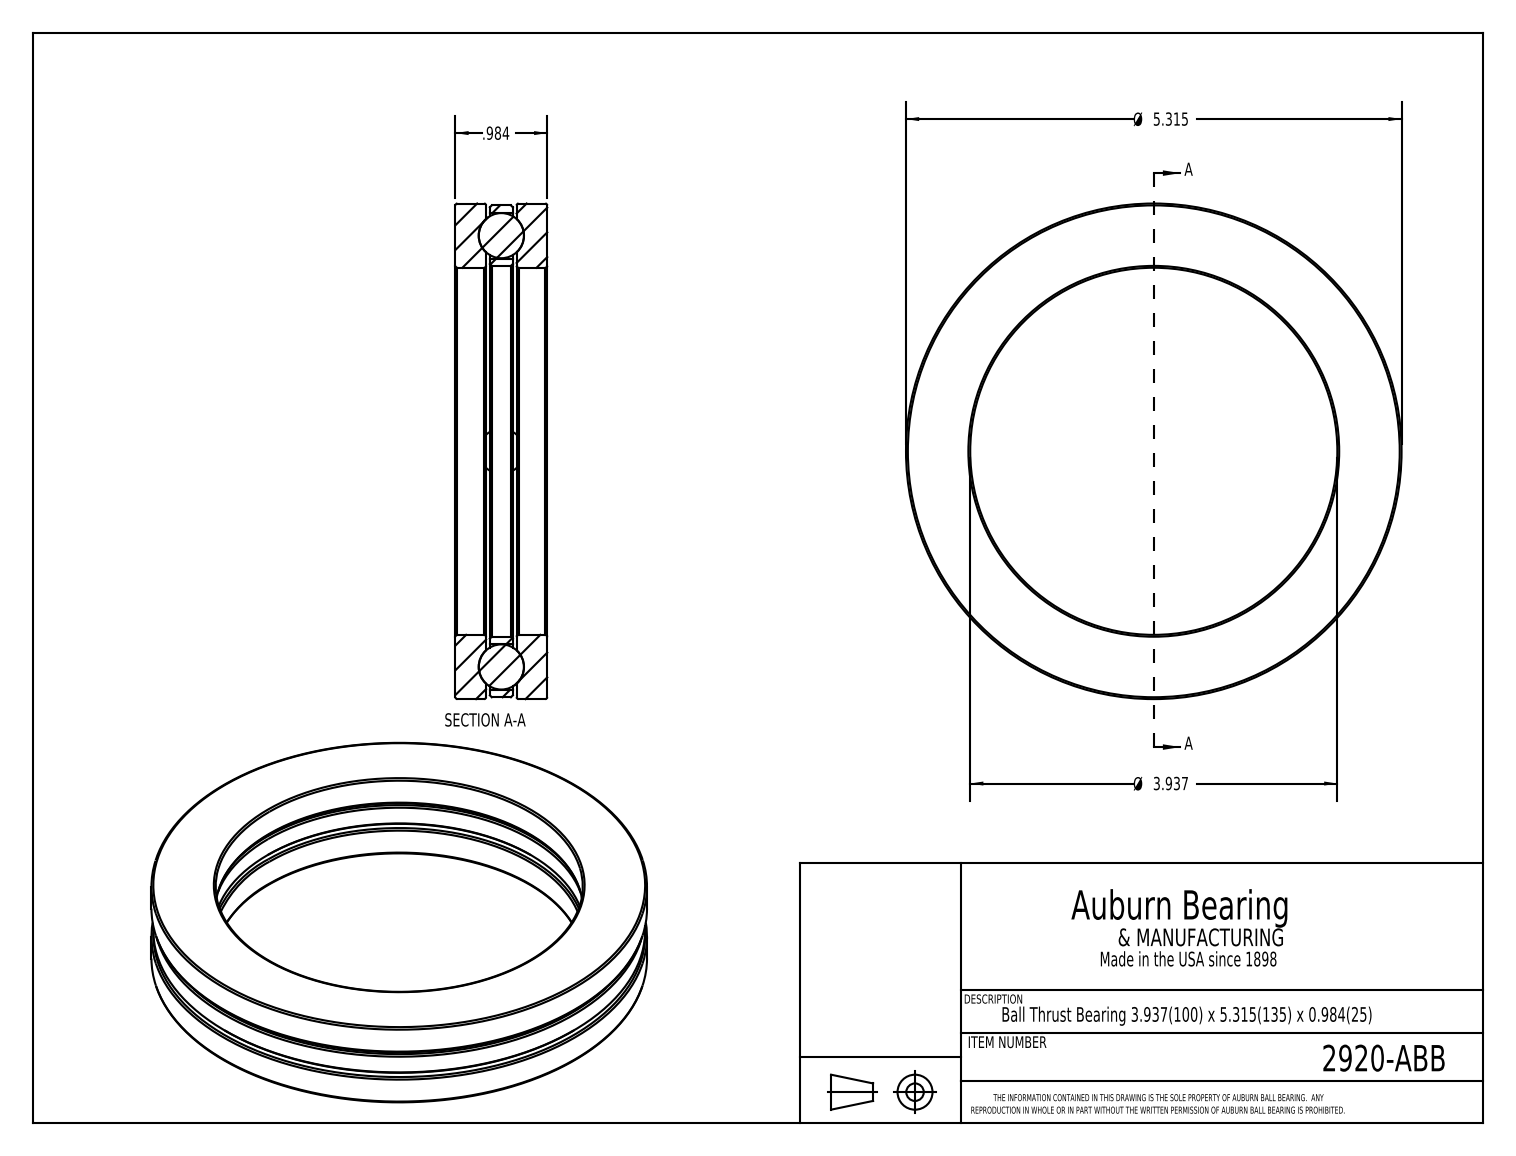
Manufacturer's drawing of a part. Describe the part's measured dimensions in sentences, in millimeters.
The part is named "2920-ABB". Its 3-D file was written by "SolidWorks 2017 (CONFIG_CONTROL_DESIGN)". It is 7 solids with 36 faces: 8 planar, 10 cylindrical and 18 other. Overall it measures 135 by 135 by 25 millimeters. Its volume is 137 000 cubic millimeters and its surface area 56 560 square millimeters. Round holes: 4 of diameter 12.5, 1 of diameter 100, 1 of diameter 101. Round bosses or shafts: 1 of diameter 135, 1 of diameter 134. The main face-to-face distances are 9.4, 15.6, 25, 8.3, 16.7, 1, 7.3, 6.2, 8.3. The hole center spacings are 58.8, 83.1, 117.5.
